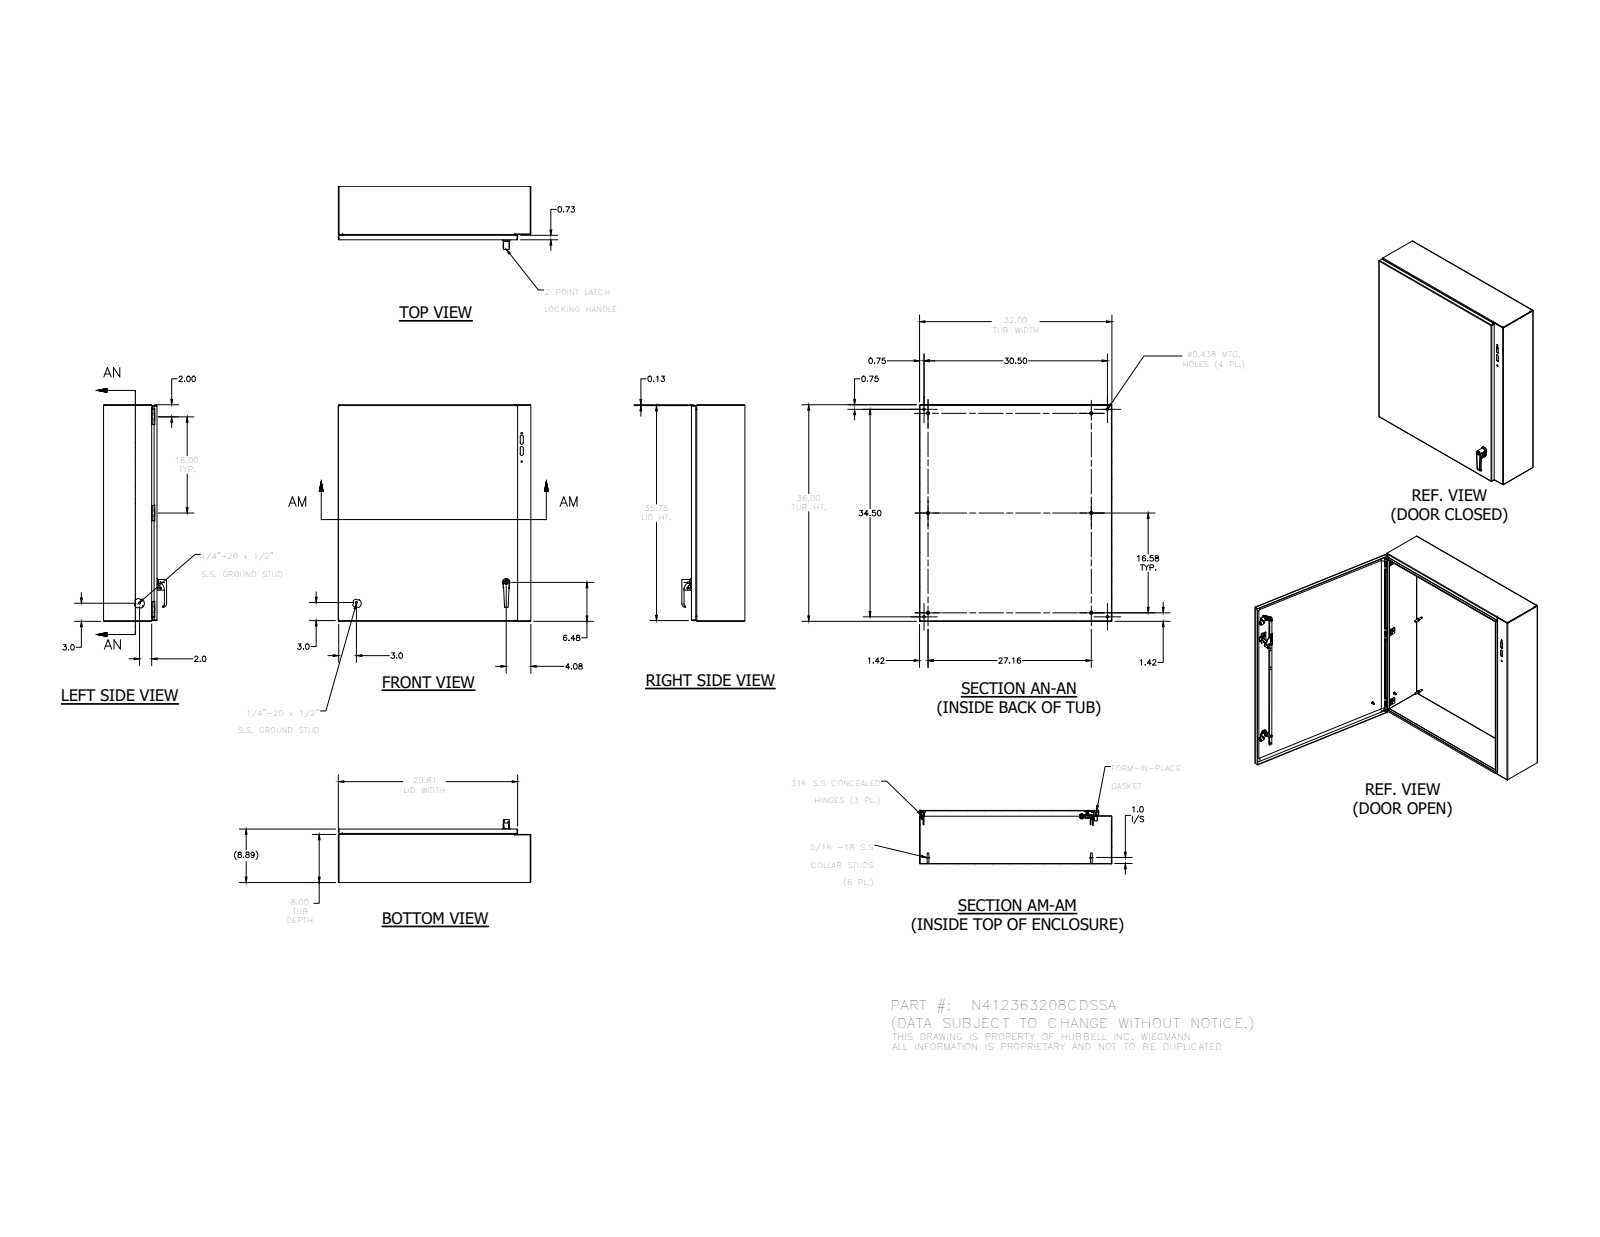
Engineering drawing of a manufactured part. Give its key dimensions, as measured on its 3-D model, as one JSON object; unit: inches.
{"part_name": "N412363208CDSSA", "step_written_by": "SolidWorks 2019 (AUTOMOTIVE_DESIGN)", "units": "inches", "bodies": {"solids": 72, "faces": 2526, "planar": 942, "cylindrical": 918, "other": 666}, "overall_size": [36, 32, 10.481], "volume_in3": 299.1, "surface_area_in2": 7656, "round_holes": [[0.093, 6], [0.145, 6], [0.152, 6], [0.167, 6], [0.172, 6], [0.187, 6], [0.156, 5], [0.437, 4], [0.32, 3], [0.196, 2], [0.211, 2], [0.22, 2]], "round_bosses_or_shafts": [[0.25, 16], [0.3, 10], [0.563, 6], [0.36, 6], [0.32, 6], [0.256, 6], [0.164, 6], [0.131, 6]], "partial_cylinders_radius": [[0.02, 38], [0.05, 38], [0.125, 33], [0.012, 30], [0.031, 30], [0.016, 26], [0.025, 16], [0.105, 16]], "face_to_face_distances": [0.074, 8.812, 8.738, 8.886, 35.926, 0.074, 7.926, 0.886, 31.852, 31.926], "hole_center_spacings": [16, 0.5, 32, 16.008, 0.656, 0.66, 1.307, 1.311]}
